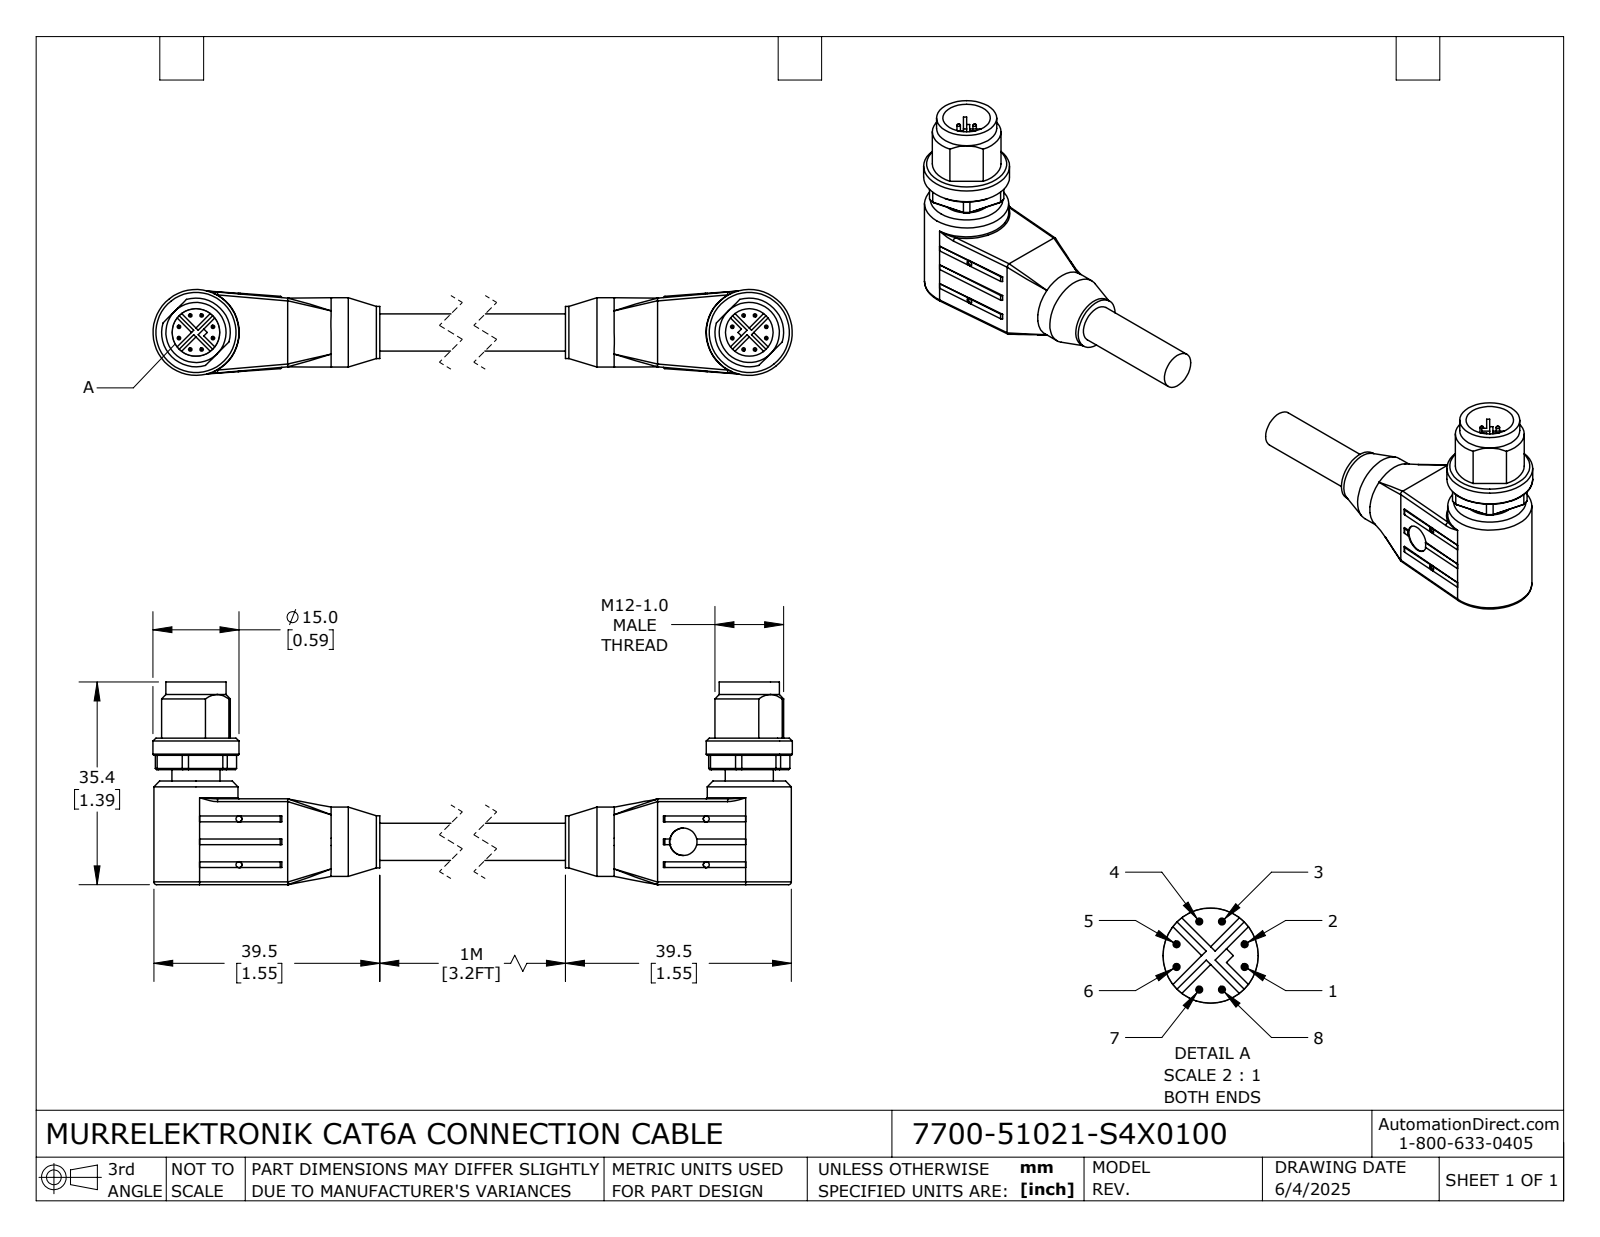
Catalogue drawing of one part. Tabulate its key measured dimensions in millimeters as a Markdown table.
| quantity | value |
| --- | --- |
| part name | 7700-51021-S4X0100_MALE; 7700-51021-S4X0100 |
| STEP written by | SolidWorks 2024 (CONFIG_CONTROL_DESIGN) |
| units | millimeters |
| bodies | 2 solids, 424 faces (196 planar, 134 cylindrical, 94 other) |
| overall size | 144.2 × 35.4 × 15 |
| volume | 18 415 mm³ |
| surface area | 8 016 mm² |
| round holes (diameter × count) | 1.05 × 8, 4.8 × 2, 8.3 × 2 |
| round bosses / shafts (diameter × count) | 0.6 × 16, 15 × 2, 14.7 × 2, 10.5 × 2, 8.4 × 2, 12.1 × 1, 9.1 × 1, 6.5 × 1 |
| partial cylindrical surfaces (radius × count) | 0.5 × 8, 0.3 × 4, 6 × 2, 7.2 × 2 |
| main face-to-face distances | 3.59, 15, 91.34, 20.1, 5.1, 18.1, 3.1, 2, 1.1, 4.7 |
| hole center spacings | 8, 114.84, 115.12, 106.88, 129.2 |
